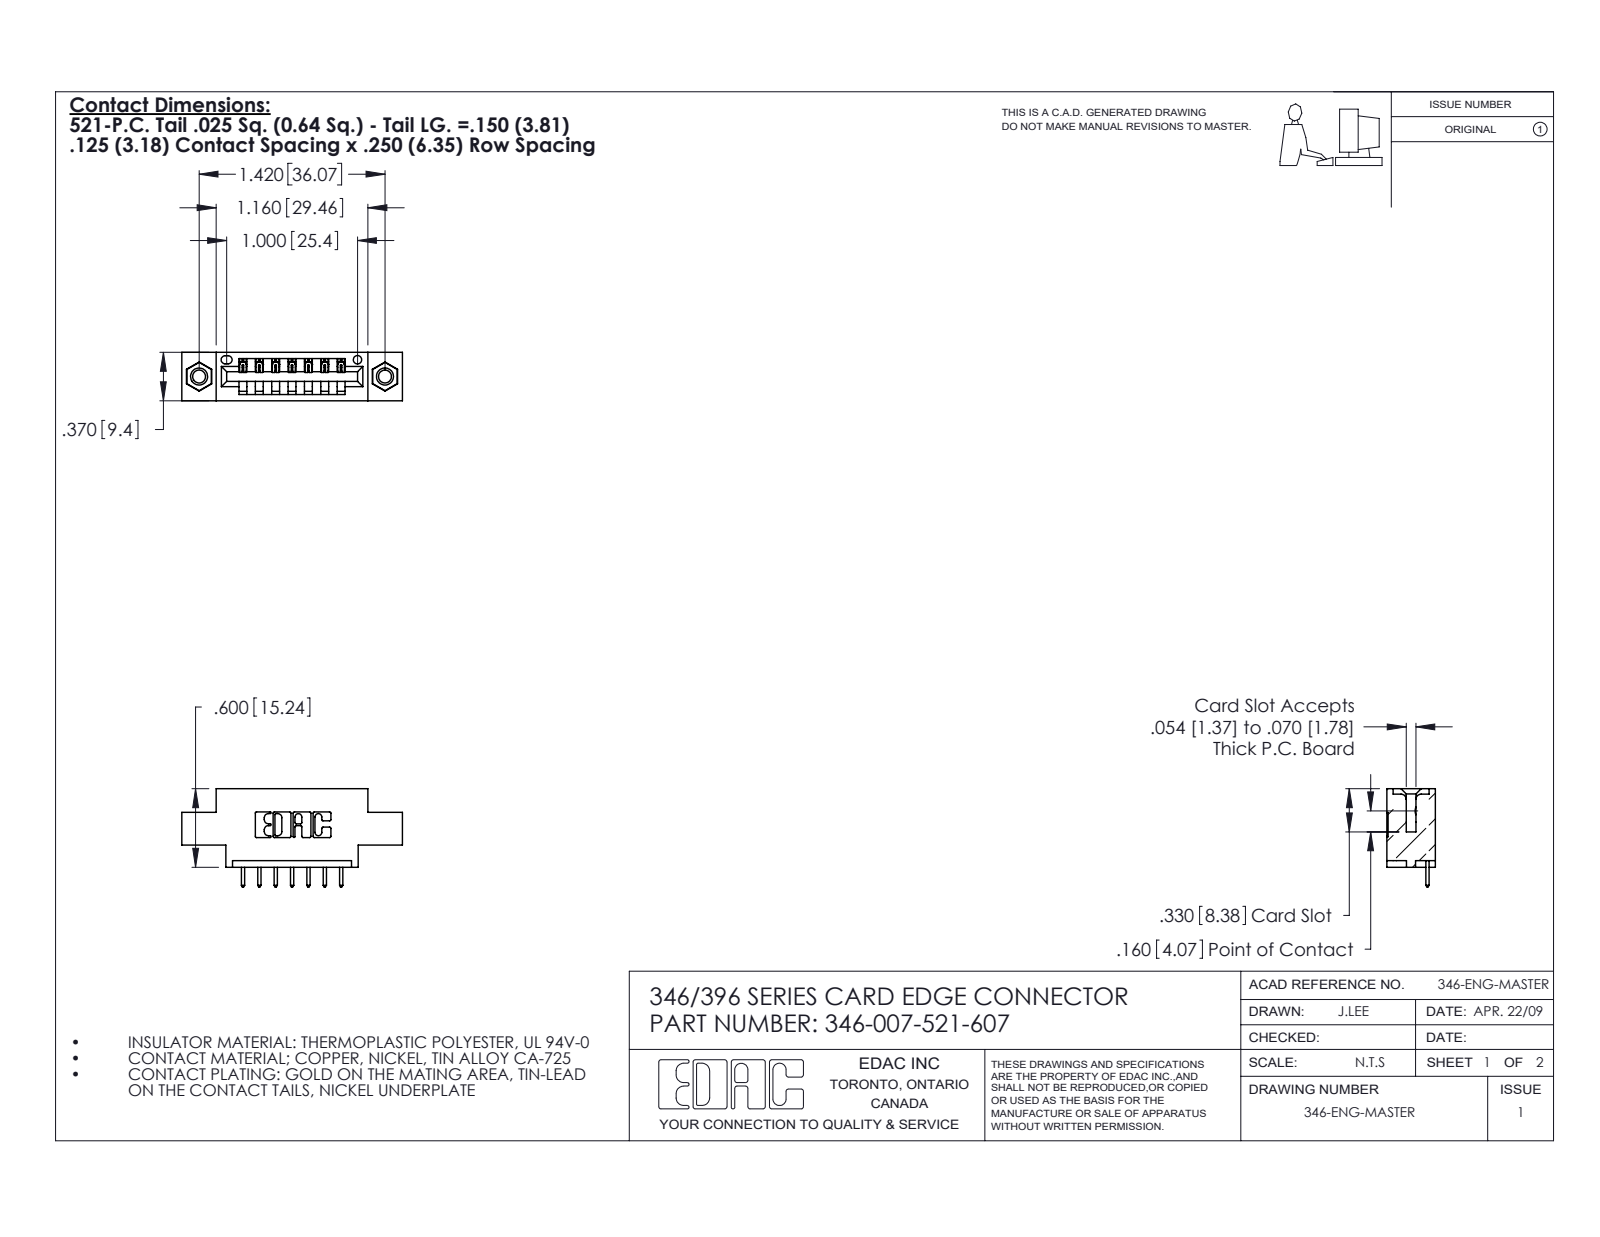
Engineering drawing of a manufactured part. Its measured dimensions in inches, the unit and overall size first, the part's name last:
Units: inches
Overall size (bounding box): 1.685 × 0.75 × 0.37
Round holes (diameter × count): ⌀0.098 ×2, ⌀0.125 ×2, ⌀0.156 ×2, ⌀0.064 ×1
Round bosses / shafts (diameter × count): ⌀0.155 ×2
Partial cylindrical surfaces — rounded edges, fillets, slot ends (radius × count): R0.01 ×22, R0.006 ×14, R0.01 ×14, R0.007 ×6, R0.031 ×6, R0.026 ×3, R0.031 ×2, R0.04 ×2
Main face-to-face distances: 0.25, 0.37, 0.048, 0.322, 0.222, 0.148, 0.1, 0.174, 0.125, 0.185
Hole centre spacings: 0.246, 1.217, 1.42
Volume: 0.224 in³ · Surface area: 6.699 in²
Bodies: 10 solids, 592 faces (392 planar, 184 cylindrical, 16 other)
Part name (STEP PRODUCT): 346 Part_0.170 Offset - 0.156 Dia-TI; 345-292-001_345-293-121; 346-007-521-607; 345-250-001_345-250-005-103
STEP written by: SolidWorks 2020 (CONFIG_CONTROL_DESIGN)
